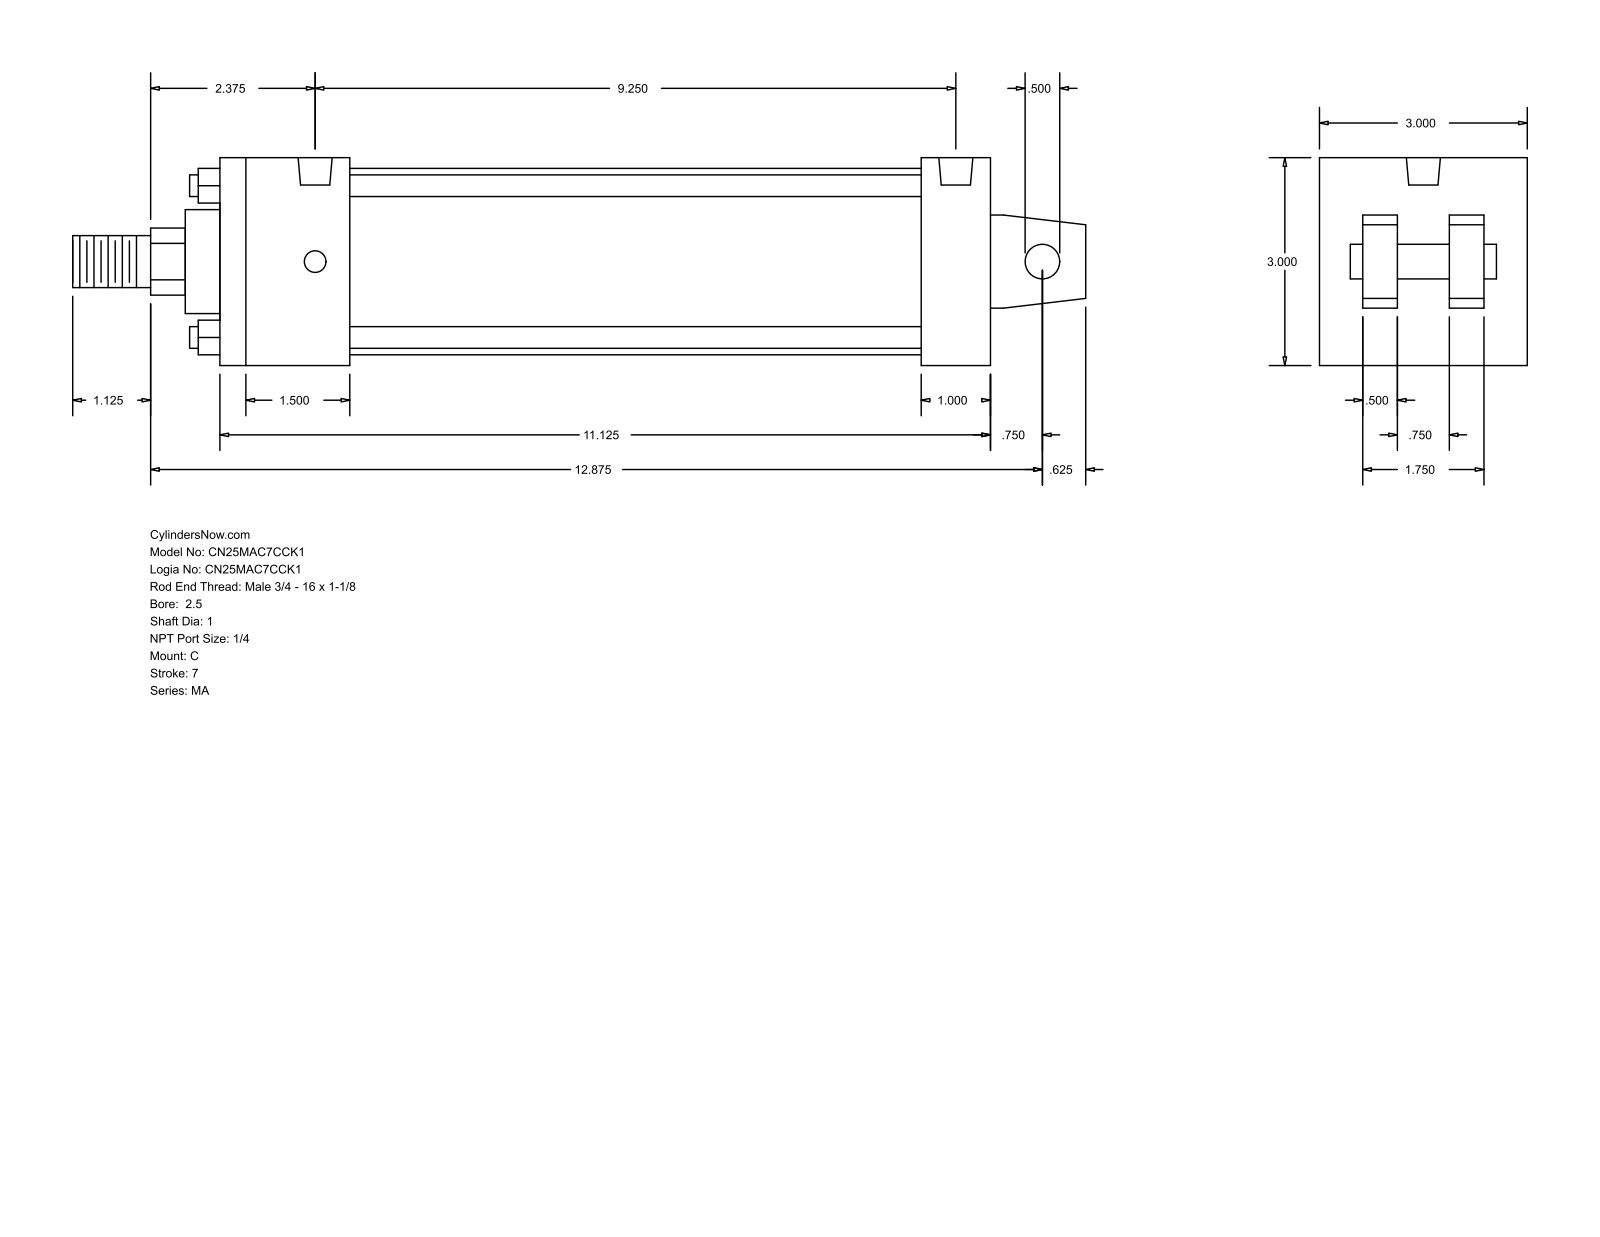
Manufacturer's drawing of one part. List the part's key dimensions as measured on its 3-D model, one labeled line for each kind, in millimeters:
Part name (STEP PRODUCT): MA_C__0250_1
STEP written by: GSSL Pune (CONFIG_CONTROL_DESIGN)
Units: millimetres
Bodies: 0 solids, 103 faces (76 planar, 27 cylindrical, 0 other)
Overall size (bounding box): 371.48 × 76.2 × 76.2
Round holes (diameter × count): ⌀7.94 ×4, ⌀12.49 ×2
Round bosses / shafts (diameter × count): ⌀7.94 ×4, ⌀68.33 ×1, ⌀38.1 ×1, ⌀25.4 ×1, ⌀19.05 ×1, ⌀12.7 ×1
Partial cylindrical surfaces — rounded edges, fillets, slot ends (radius × count): R12.29 ×1
Main face-to-face distances: 76.2, 47.63, 282.58, 12.7, 60.33, 15.87, 28.57, 257.17, 209.54, 234.95
Hole centre spacings: 234.94
